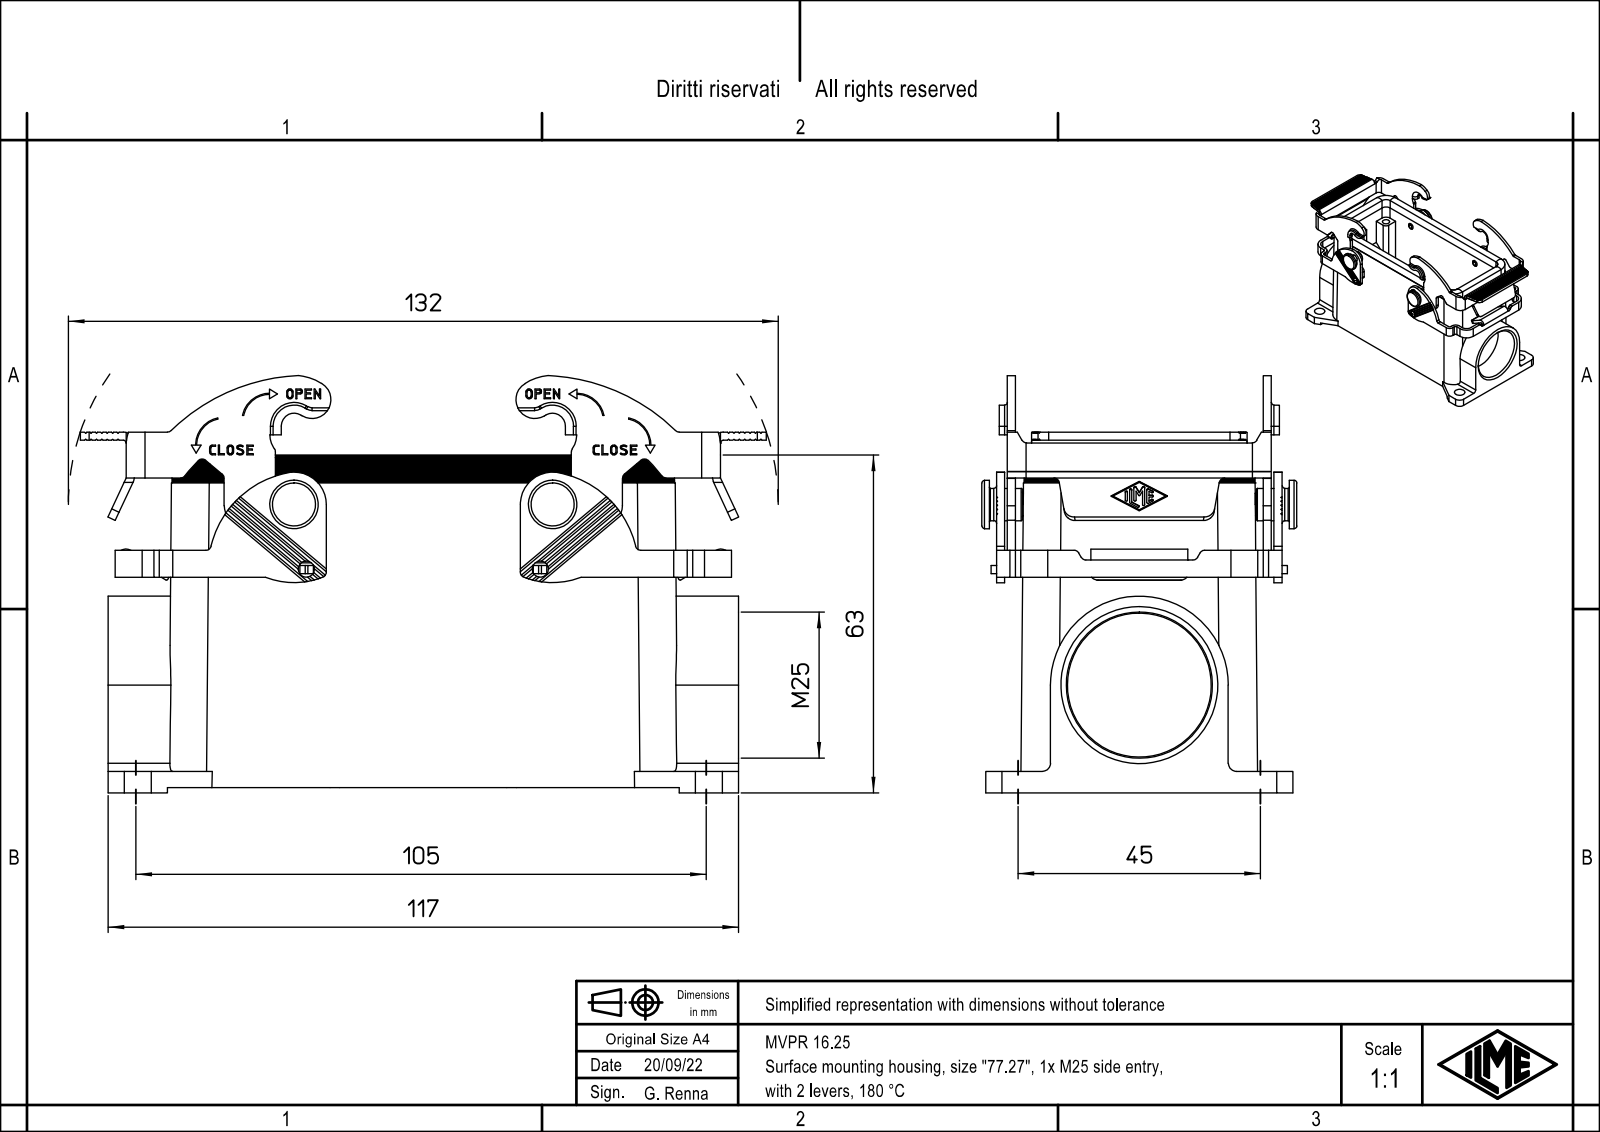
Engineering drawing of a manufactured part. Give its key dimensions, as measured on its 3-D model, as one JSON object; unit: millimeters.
{"part_name": "MVPR 16.25", "step_written_by": "Creo Elements/Direct Modeling 20.1B 02-Apr-2019 (C) Parametric Technology GmbH (AUTOMOTIVE_DESIGN)", "units": "millimeters", "bodies": {"solids": 1, "faces": 1058, "planar": 576, "cylindrical": 360, "other": 122}, "overall_size": [127.33, 77.4, 58.47], "volume_mm3": 107399, "surface_area_mm2": 65241, "round_holes": [[3.8, 4], [5.5, 4], [7.9, 4], [3, 2], [3.25, 2], [6.2, 2], [21, 1]], "round_bosses_or_shafts": [[9, 2], [6, 2]], "partial_cylinders_radius": [[1, 44], [2, 40], [0.5, 19], [0.25, 15], [3, 14], [3.5, 12], [1.5, 8], [2.5, 8]], "face_to_face_distances": [1.5, 2, 49.5, 3, 47.5, 0.5, 48, 51, 3.5, 51.5], "hole_center_spacings": [3.38, 13.6, 16.43, 30.04, 38.54, 40.86, 79.11, 84.55]}
